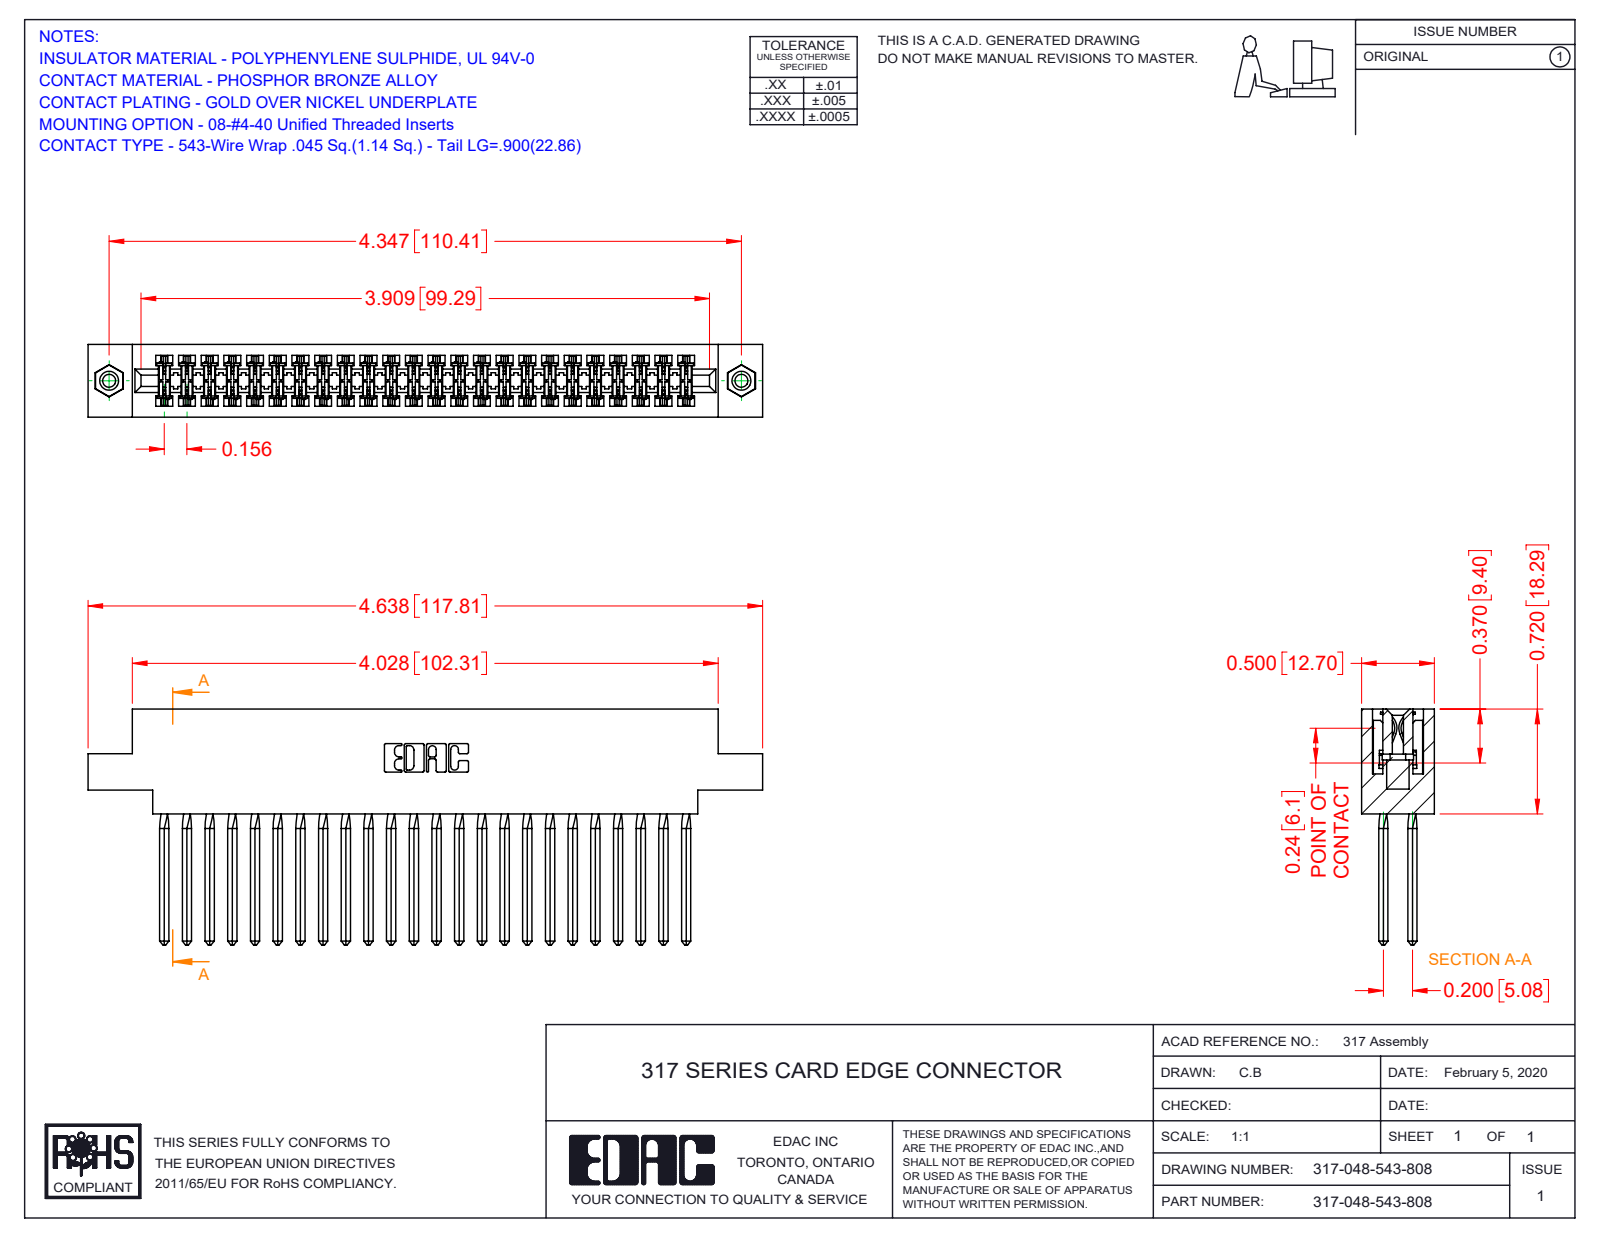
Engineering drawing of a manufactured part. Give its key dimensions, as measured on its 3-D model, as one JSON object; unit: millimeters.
{"part_name": "317 Part_.156 Dia - TI; 317-048-543-808; 317-290-001_543; 345-250-001_345-250-003-102", "step_written_by": "SolidWorks 2016 (CONFIG_CONTROL_DESIGN)", "units": "millimeters", "bodies": {"solids": 51, "faces": 4434, "planar": 3594, "cylindrical": 632, "other": 208}, "overall_size": [117.8, 41.1, 12.7], "volume_mm3": 19400, "surface_area_mm2": 28740, "round_holes": [[2.3, 2], [3.2, 2], [4, 2]], "round_bosses_or_shafts": [[3.9, 2]], "partial_cylinders_radius": [[0.4, 96], [0.3, 22], [0.2, 6], [0.8, 6], [0.7, 3], [2.4, 2], [2.5, 2], [2.8, 2]], "face_to_face_distances": [12.7, 1.9, 10.8, 2.8, 8.9, 5, 5.6, 2.4, 18.3, 5.1], "hole_center_spacings": [110.4]}
